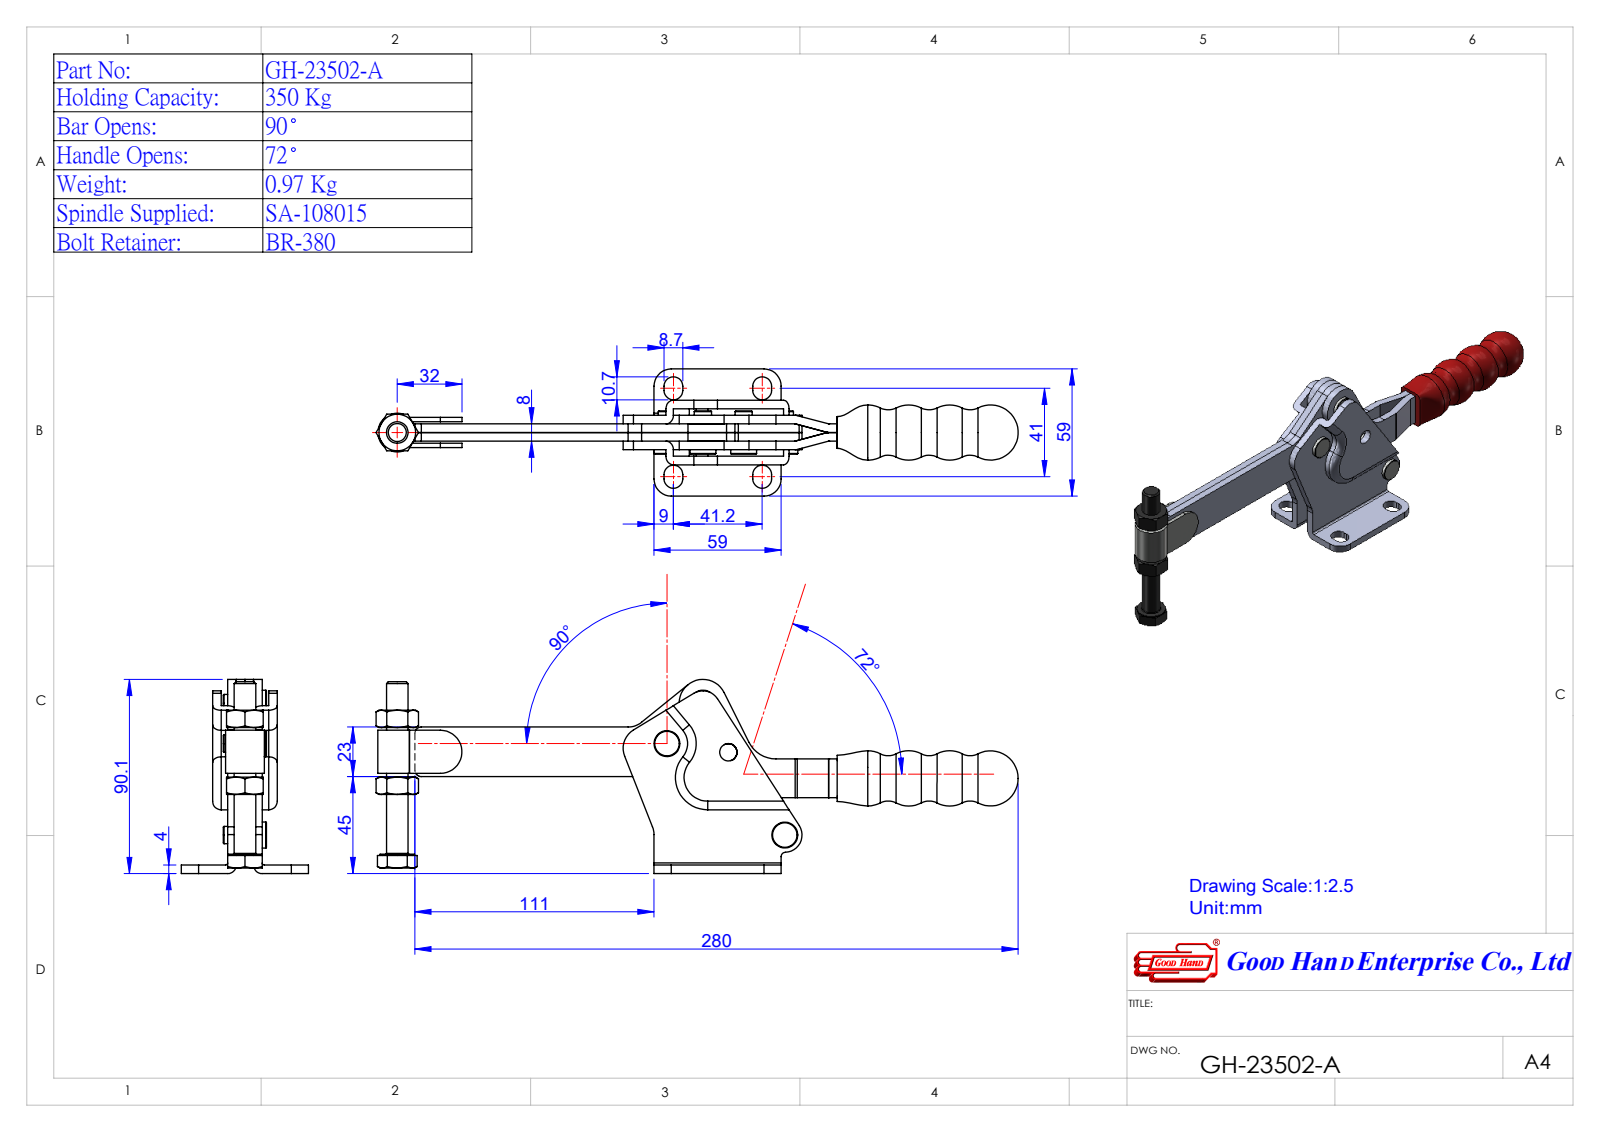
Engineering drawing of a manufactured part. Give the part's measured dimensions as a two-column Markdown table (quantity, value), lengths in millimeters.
| quantity | value |
| --- | --- |
| part name | Group4^GH-23502-A(簡化); GH-23502-A(簡化); Group2^GH-23501-A(簡化); Group3^GH-23502-A(簡化) (+2 more) |
| STEP written by | SolidWorks 2016 (AUTOMOTIVE_DESIGN) |
| units | millimeters |
| bodies | 5 solids, 310 faces (124 planar, 112 cylindrical, 74 other) |
| overall size | 299.87 × 106.24 × 59 |
| volume | 165 944 mm³ |
| surface area | 66 709 mm² |
| round holes (diameter × count) | 5 × 2, 6 × 2, 8 × 1 |
| round bosses / shafts (diameter × count) | 5 × 2, 22.7 × 1, 16 × 1, 10 × 1 |
| partial cylindrical surfaces (radius × count) | 4.35 × 8, 8 × 6, 1 × 4, 2 × 4, 10 × 3, 11 × 2, 14 × 2, 3 × 1 |
| main face-to-face distances | 4, 8, 12, 7, 19, 11, 16, 23, 3, 15 |
| hole center spacings | 12.42, 25.15, 25.67, 28.78, 34.07, 38.02, 38.32, 46.49 |
